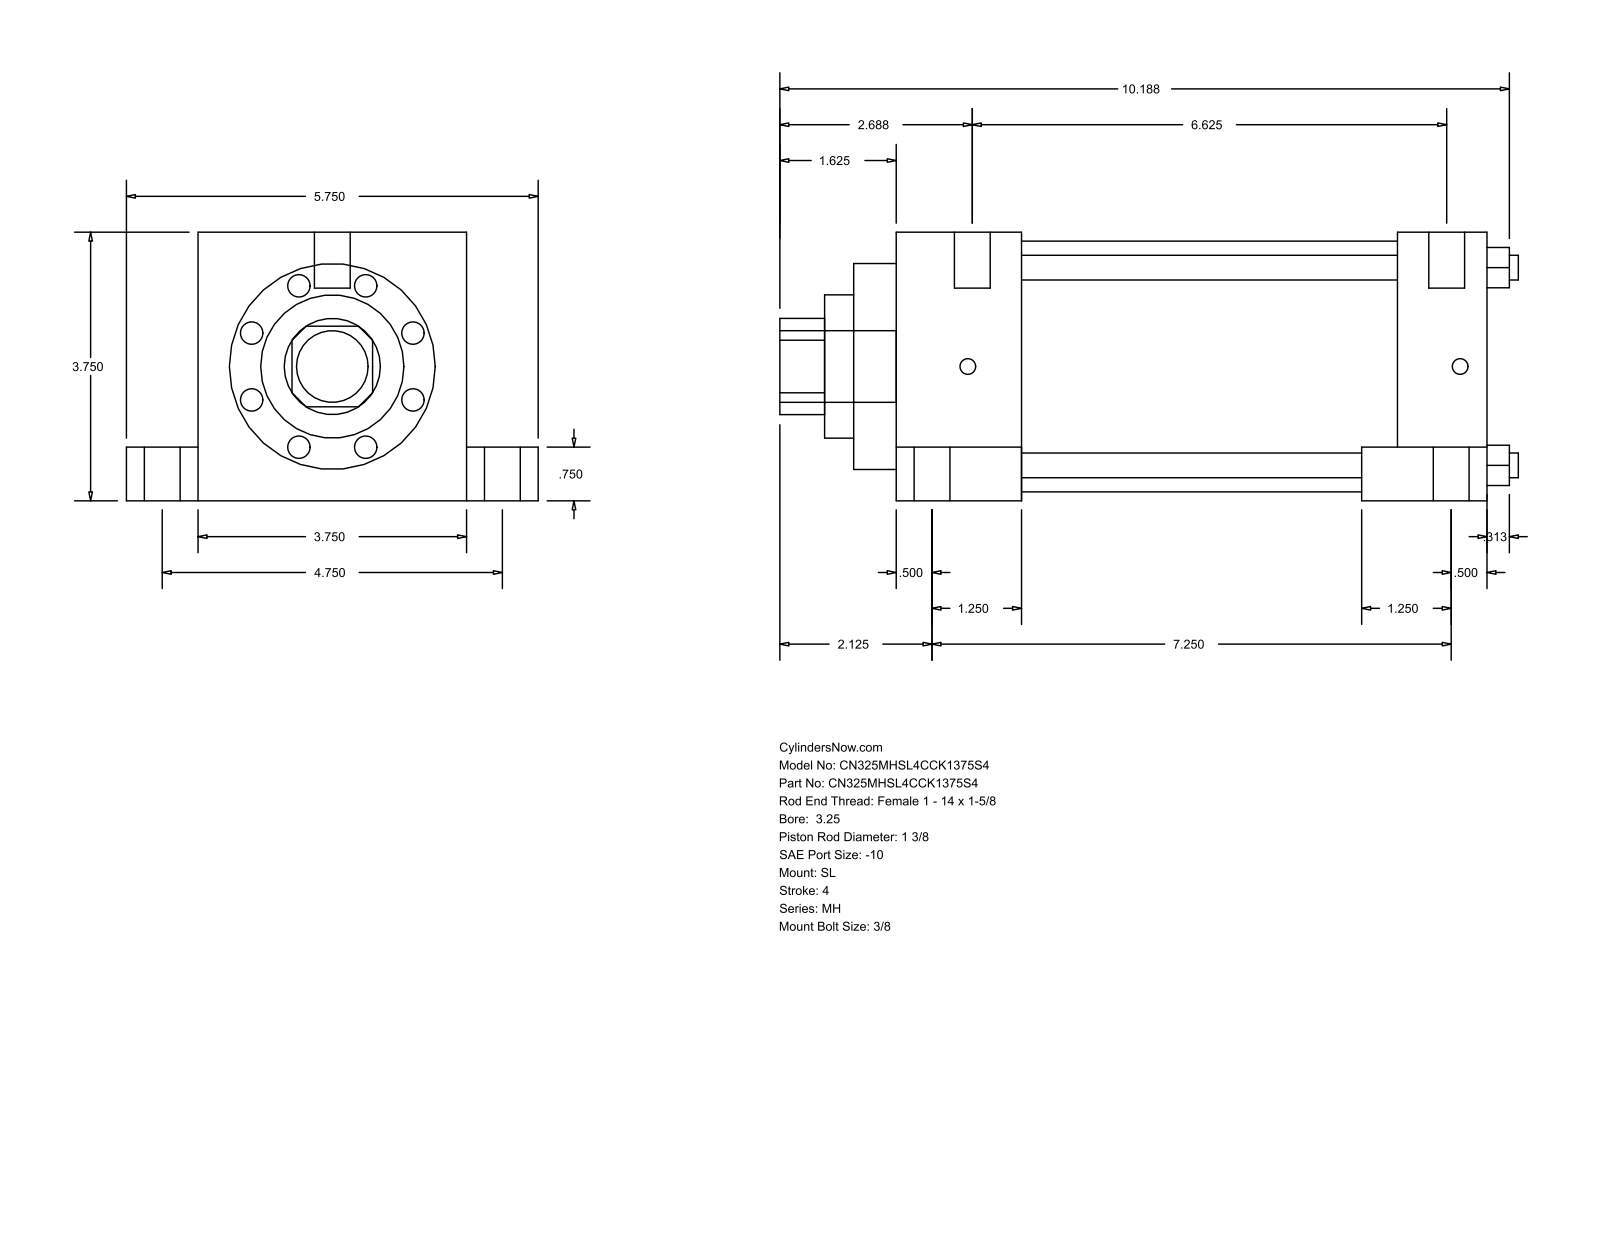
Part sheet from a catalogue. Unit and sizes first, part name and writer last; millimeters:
Units: millimetres
Overall size (bounding box): 261.94 × 146.05 × 95.25
Round holes (diameter × count): ⌀8.76 ×4, ⌀34.92 ×1, ⌀50.8 ×1, ⌀73.03 ×1, ⌀88.9 ×1
Round bosses / shafts (diameter × count): ⌀12.7 ×6, ⌀19.05 ×4, ⌀5.56 ×4, ⌀25.4 ×1
Partial cylindrical surfaces — rounded edges, fillets, slot ends (radius × count): R17.06 ×1
Main face-to-face distances: 95.24, 209.55, 44.45, 165.1, 25.41, 120.65, 19.05, 76.19, 177.8, 133.35
Hole centre spacings: 49.57, 70.1, 99.14
Bodies: 0 solids, 110 faces (77 planar, 33 cylindrical, 0 other)
Part name (STEP PRODUCT): MH_SL__0325_1.375
STEP written by: GSSL Pune (CONFIG_CONTROL_DESIGN)
